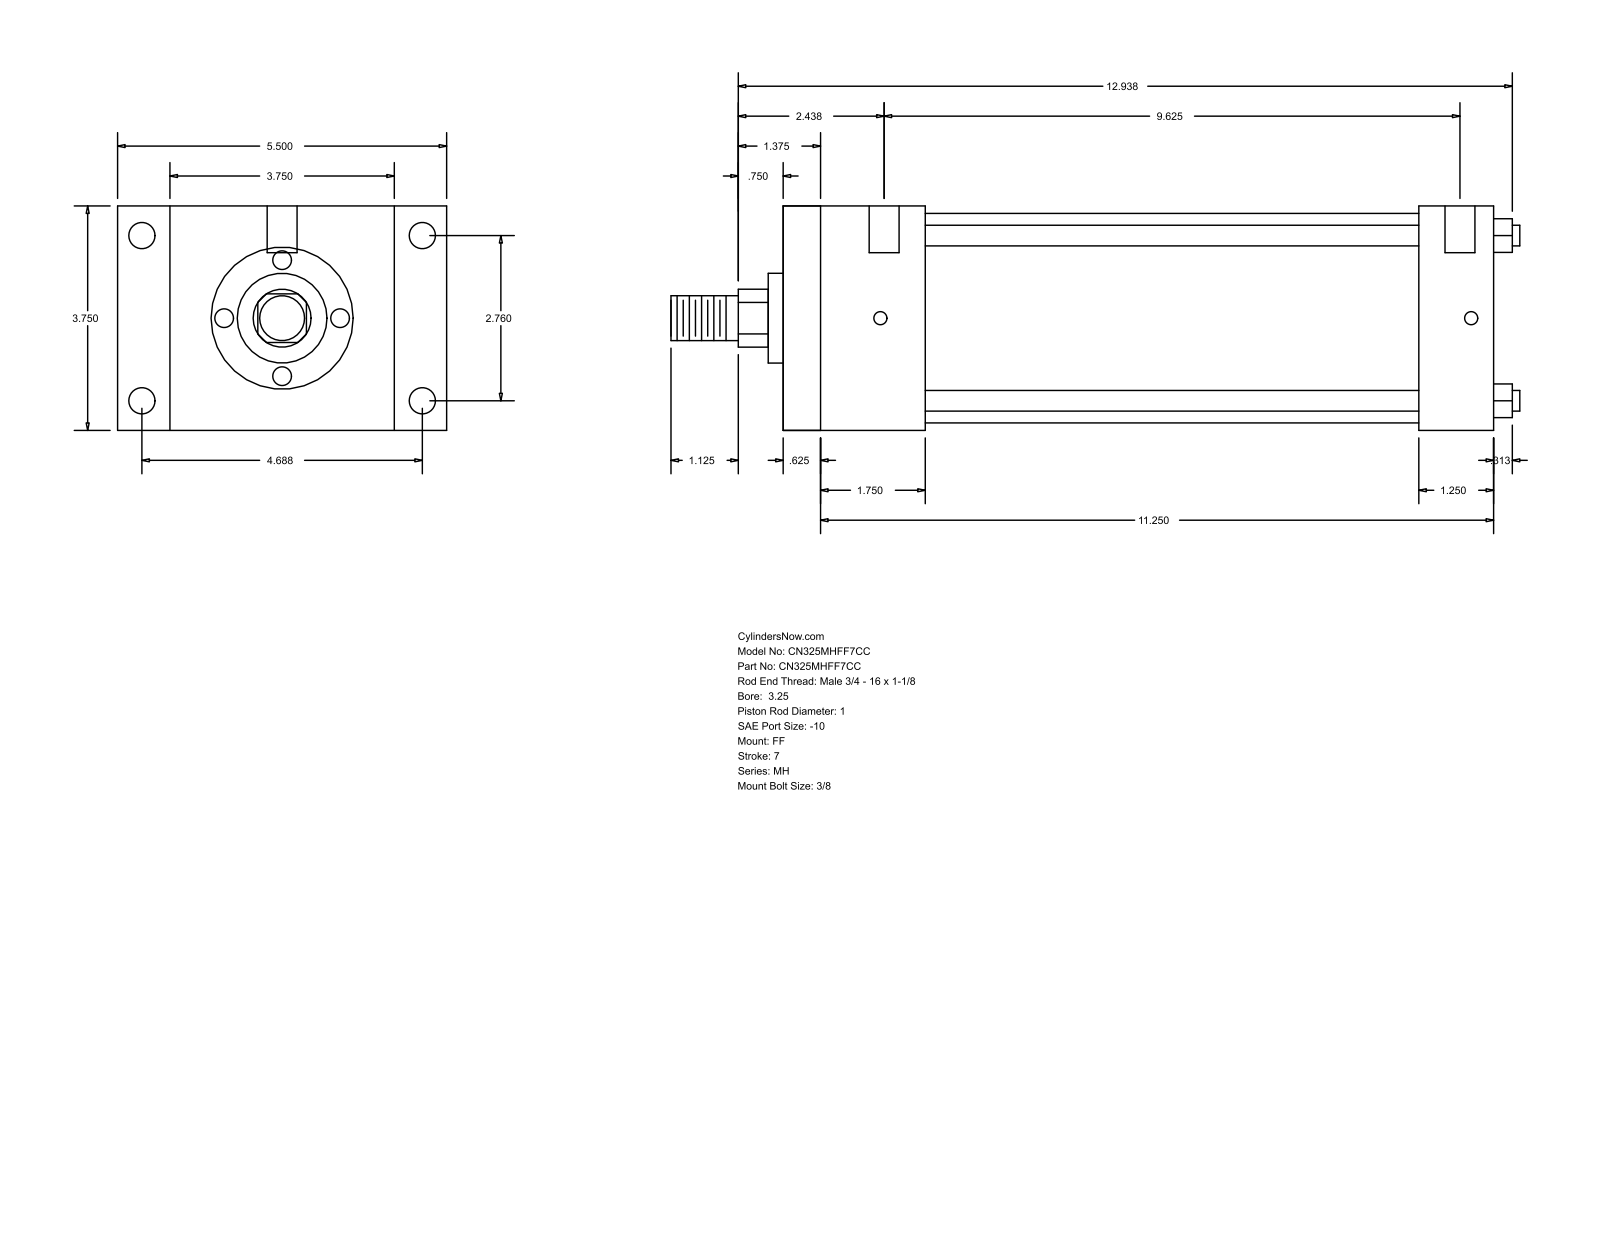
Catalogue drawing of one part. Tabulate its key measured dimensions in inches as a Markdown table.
| quantity | value |
| --- | --- |
| part name | MH_FF__0325_1 |
| STEP written by | GSSL Pune (CONFIG_CONTROL_DESIGN) |
| units | inches |
| bodies | 0 solids, 92 faces (64 planar, 28 cylindrical, 0 other) |
| overall size | 14.187 × 5.5 × 3.75 |
| round holes (diameter × count) | 0.219 × 4, 0.438 × 4, 0.5 × 2 |
| round bosses / shafts (diameter × count) | 0.345 × 4, 3.5 × 1, 1.5 × 1, 1 × 1, 0.75 × 1 |
| partial cylindrical surfaces (radius × count) | 0.484 × 1 |
| main face-to-face distances | 3.75, 11.875, 0.625, 11.25, 0.875, 4.625, 10.625, 10, 1.25, 2.375 |
| hole center spacings | 2.76, 4.687, 5.439, 9.875, 0.062, 0.187, 9.625, 9.687 |
